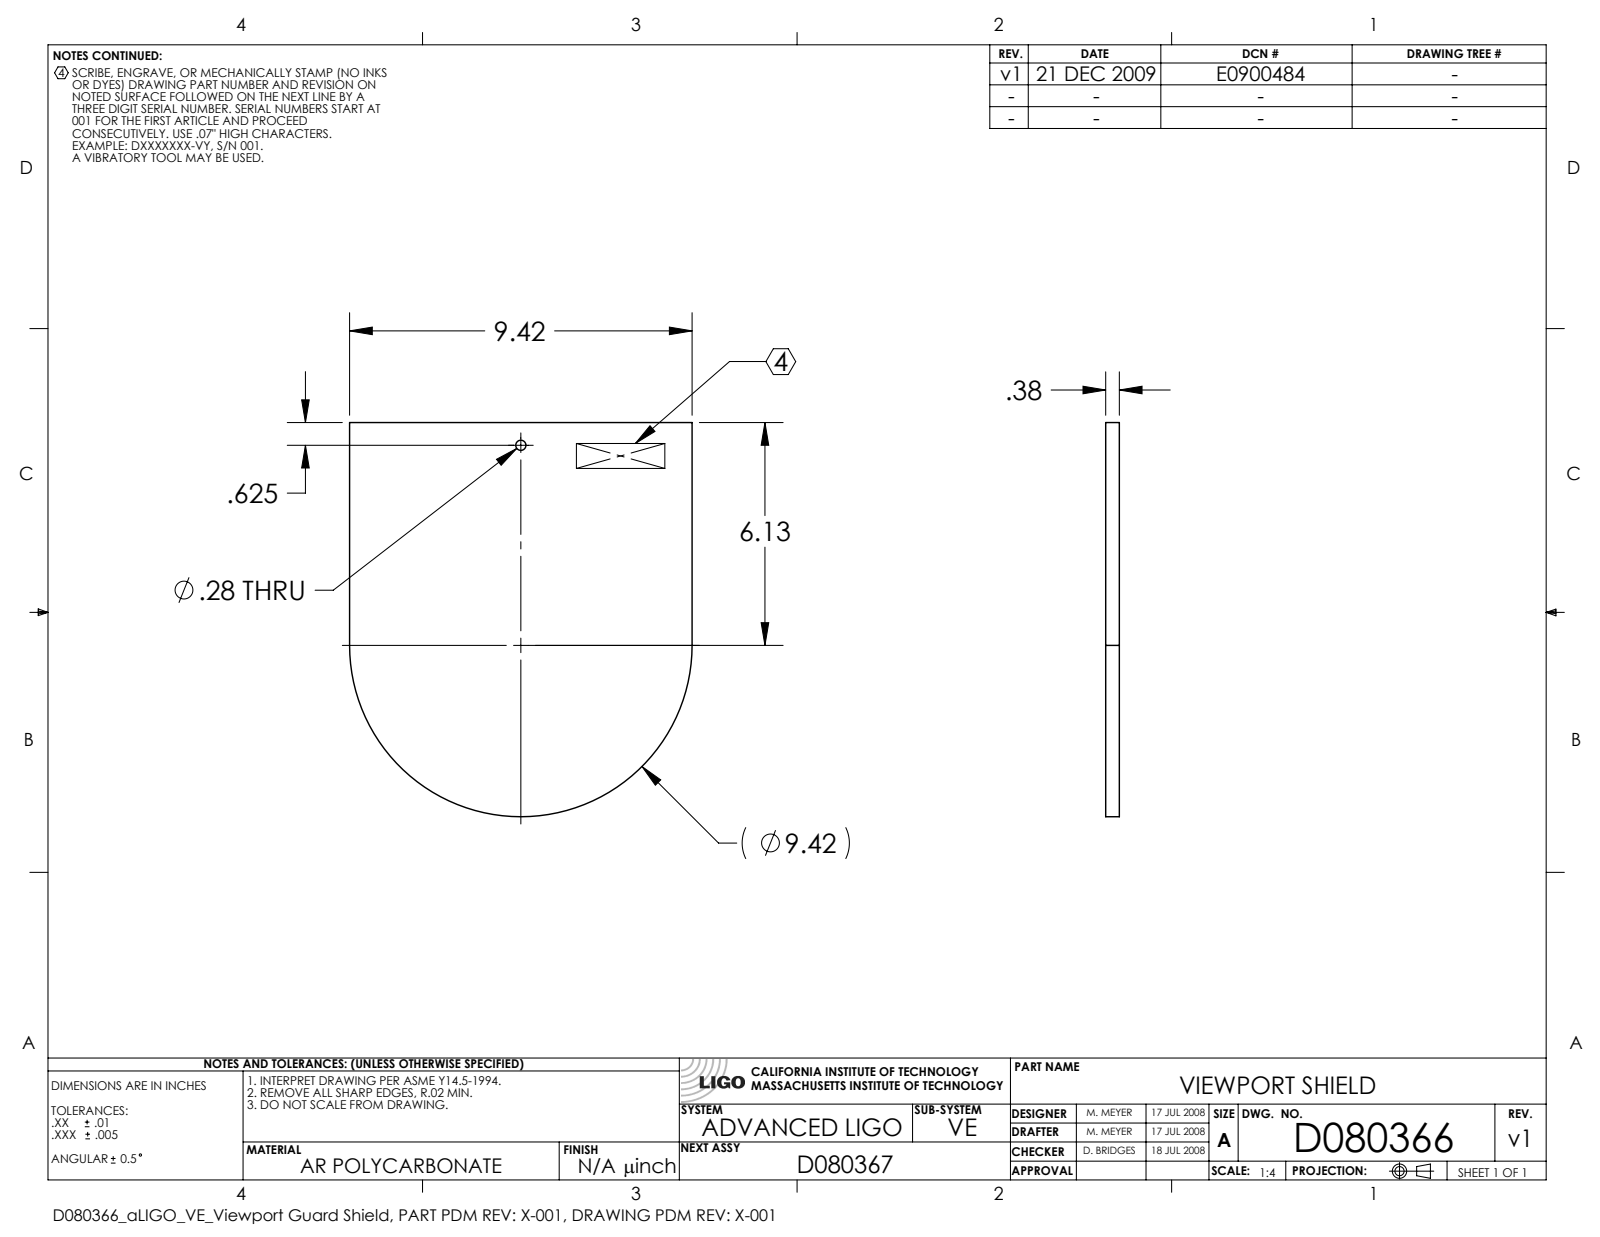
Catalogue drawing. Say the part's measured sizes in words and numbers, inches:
The part is named "D080366-v1_aLIGO_VE_Viewport Guard Shield". Its 3-D file was written by "SolidWorks 2009 (CONFIG_CONTROL_DESIGN)". It is 1 solid with 8 faces: 5 planar, 3 cylindrical and 0 other. Overall it measures 10.834 by 9.419 by 0.375 inches. Its volume is 34.67 cubic inches and its surface area 198.9 square inches. Round holes: 1 of diameter 0.281. Partial cylindrical surfaces (rounded edges, fillets, slot ends): 1 of radius 4.709. The main face-to-face distances are 0.375, 9.419.
